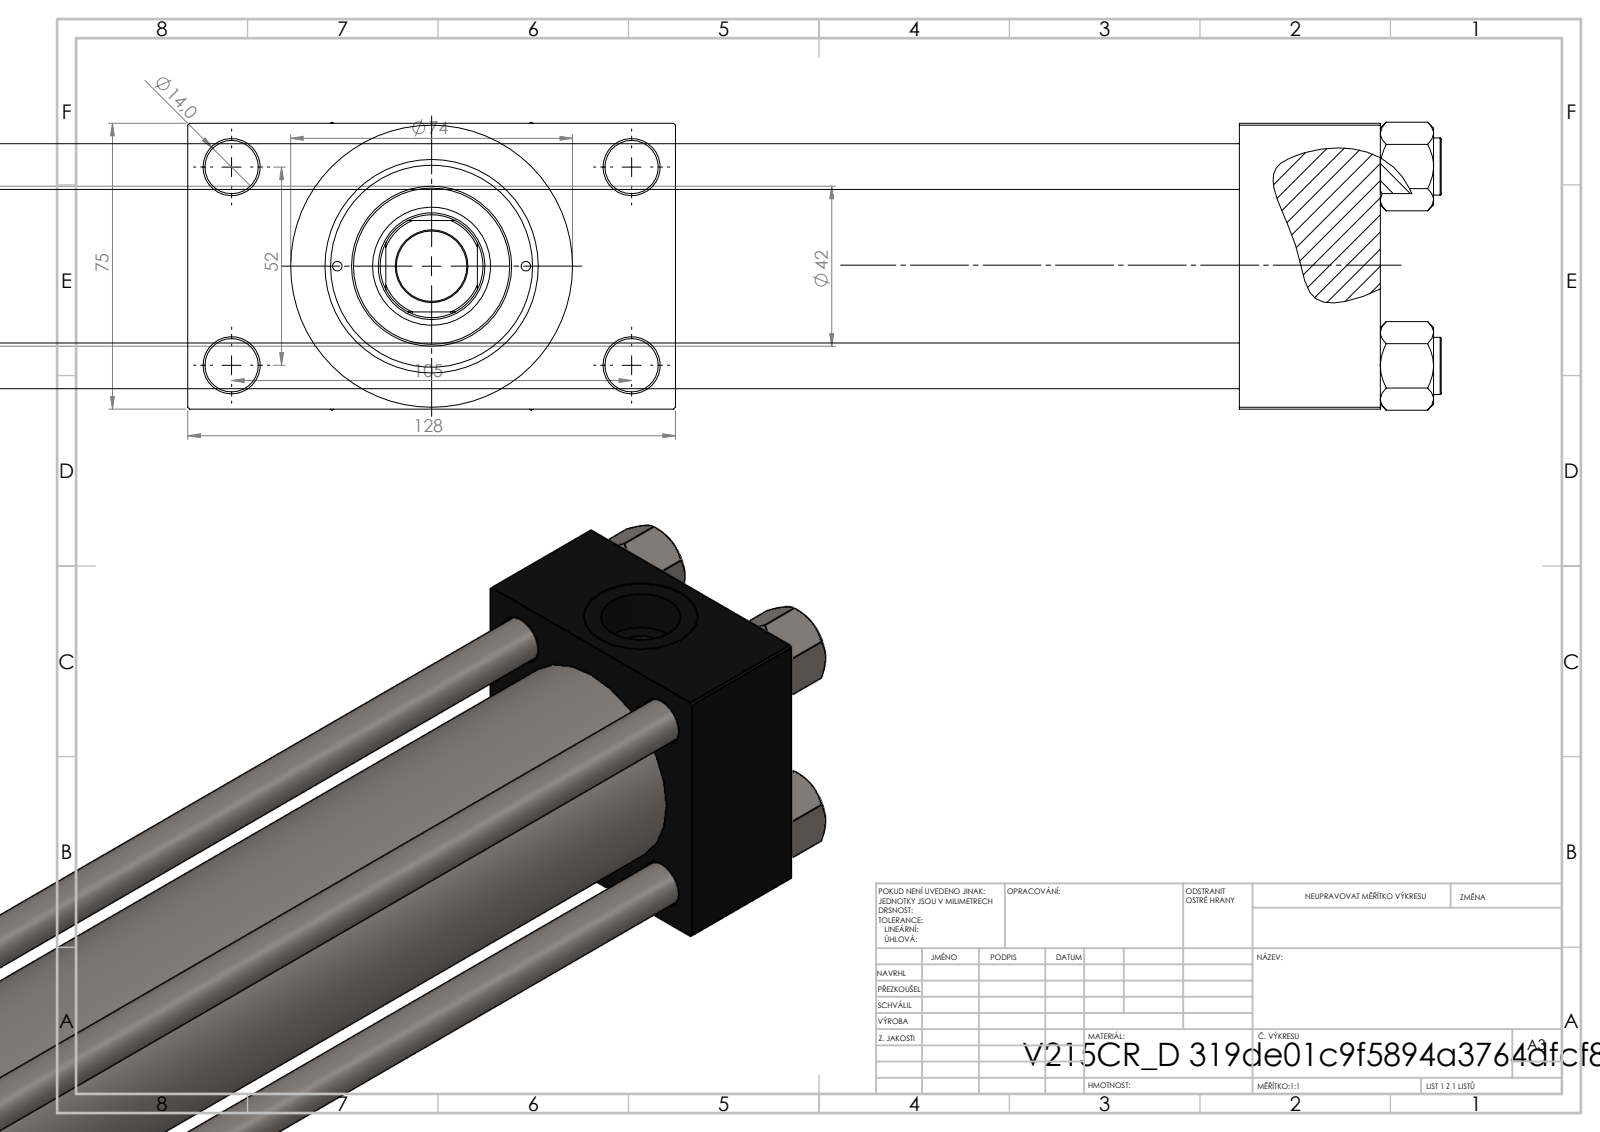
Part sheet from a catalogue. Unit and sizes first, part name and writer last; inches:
Units: inches
Overall size (bounding box): 30.512 × 5.039 × 2.974
Round holes (diameter × count): ⌀0.472 ×4, ⌀0.551 ×4, ⌀0.098 ×2, ⌀0.276 ×2, ⌀0.825 ×2, ⌀1.181 ×2, ⌀0.728 ×1, ⌀1.102 ×1, ⌀1.22 ×1, ⌀1.614 ×1, ⌀1.969 ×1, ⌀2.087 ×1
Round bosses / shafts (diameter × count): ⌀0.591 ×4, ⌀2.913 ×1, ⌀2.205 ×1, ⌀1.654 ×1
Partial cylindrical surfaces — rounded edges, fillets, slot ends (radius × count): R0.531 ×1
Main face-to-face distances: 2.953, 25.118, 1.457, 26.575, 1.043, 3.996, 28.268, 26.811, 1.693, 0.63
Hole centre spacings: 1.031, 1.037, 1.456, 1.497, 2.059, 2.253, 2.3, 2.307
Volume: 105.2 in³ · Surface area: 775.7 in²
Bodies: 11 solids, 1112 faces (499 planar, 93 cylindrical, 520 other)
Part name (STEP PRODUCT): V215CR_D_Body; NUT_M5_D; V215CR_VCP_D; V215CR_D_TYCINKA (+1 more)
STEP written by: SolidWorks 2019 (CONFIG_CONTROL_DESIGN)
